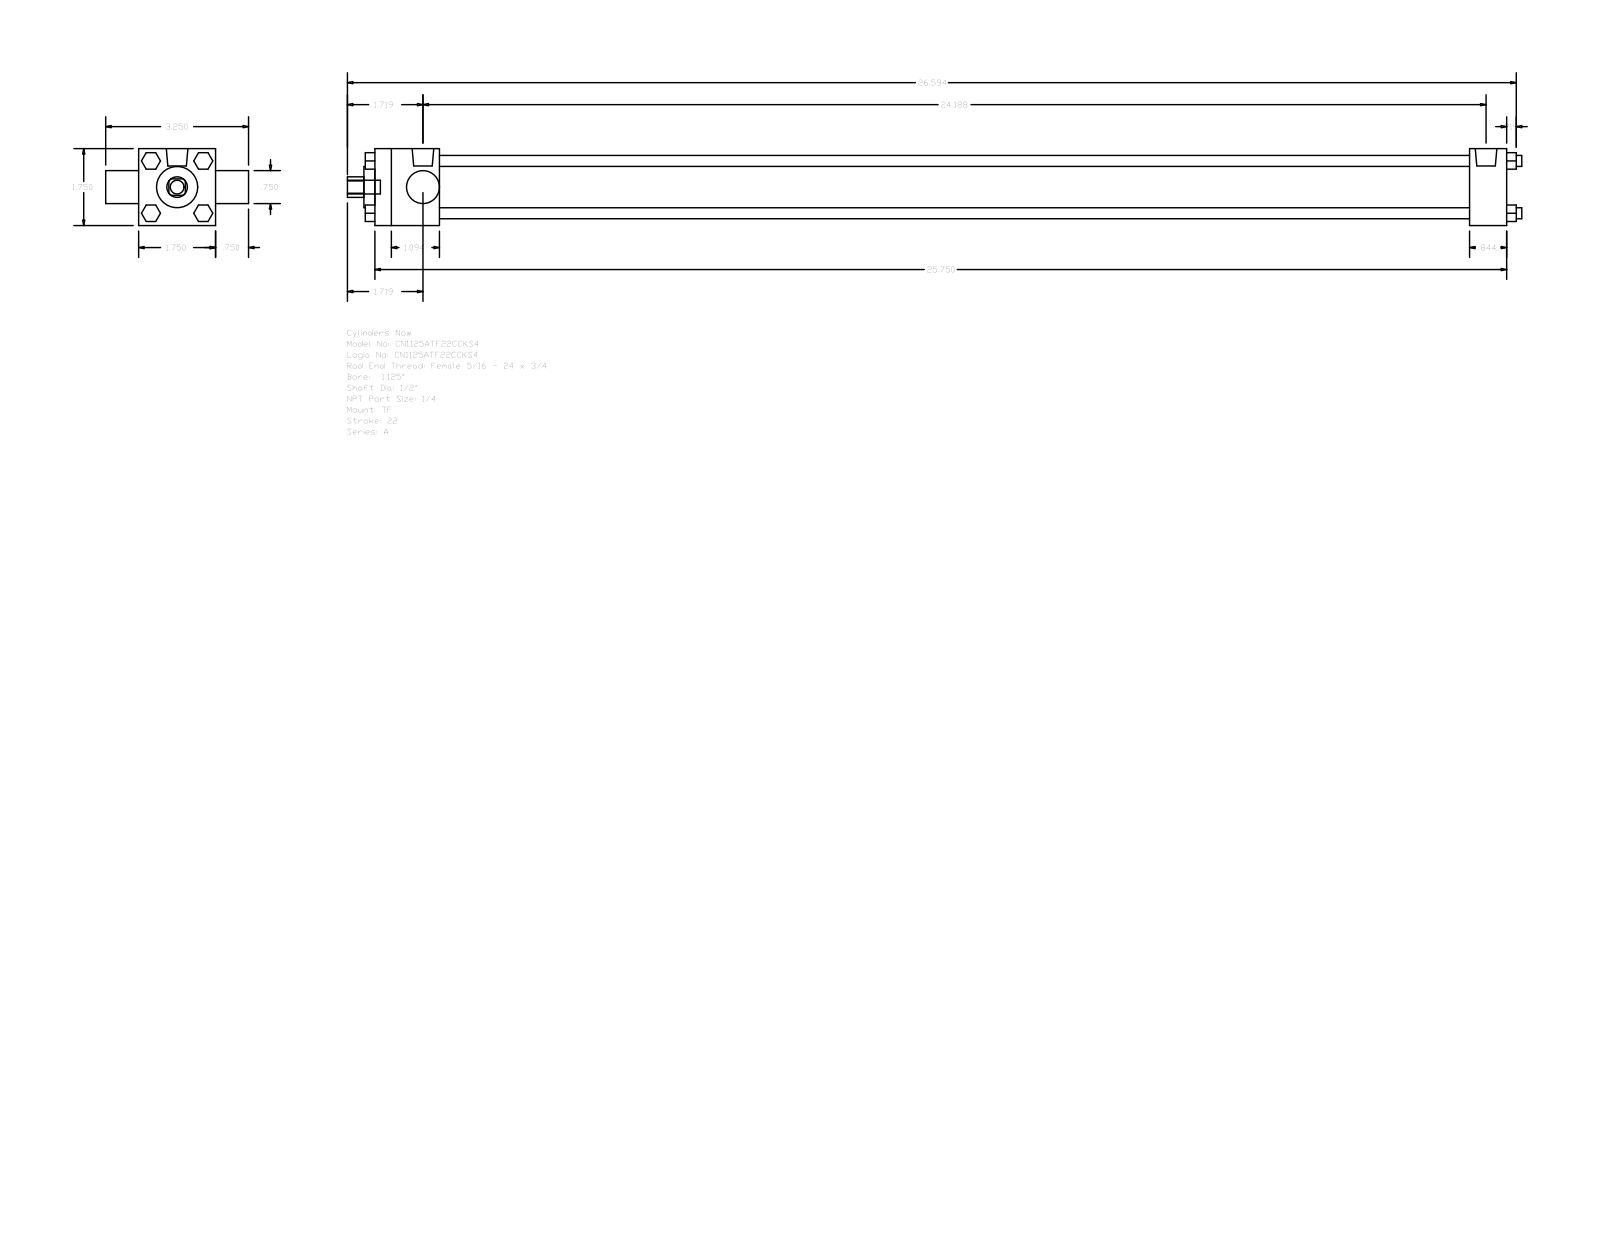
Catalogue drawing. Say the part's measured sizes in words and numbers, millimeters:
The part is named "A_TF__0112_0.5". Its 3-D file was written by "GSSL Pune (CONFIG_CONTROL_DESIGN)". It is 0 solids with 120 faces: 92 planar, 28 cylindrical and 0 other. Overall it measures 678.66 by 82.55 by 44.45 millimeters. Round holes: 1 of diameter 12.7, 1 of diameter 19.05, 1 of diameter 23.81, 1 of diameter 31.88. Round bosses or shafts: 4 of diameter 6.35, 3 of diameter 5.56, 2 of diameter 12.49, 1 of diameter 7.94. Partial cylindrical surfaces (rounded edges, fillets, slot ends): 1 of radius 5.94. The main face-to-face distances are 44.46, 654.04, 632.61, 21.43, 37.3, 595.31, 616.74, 19.04, 63.5, 9.53.
